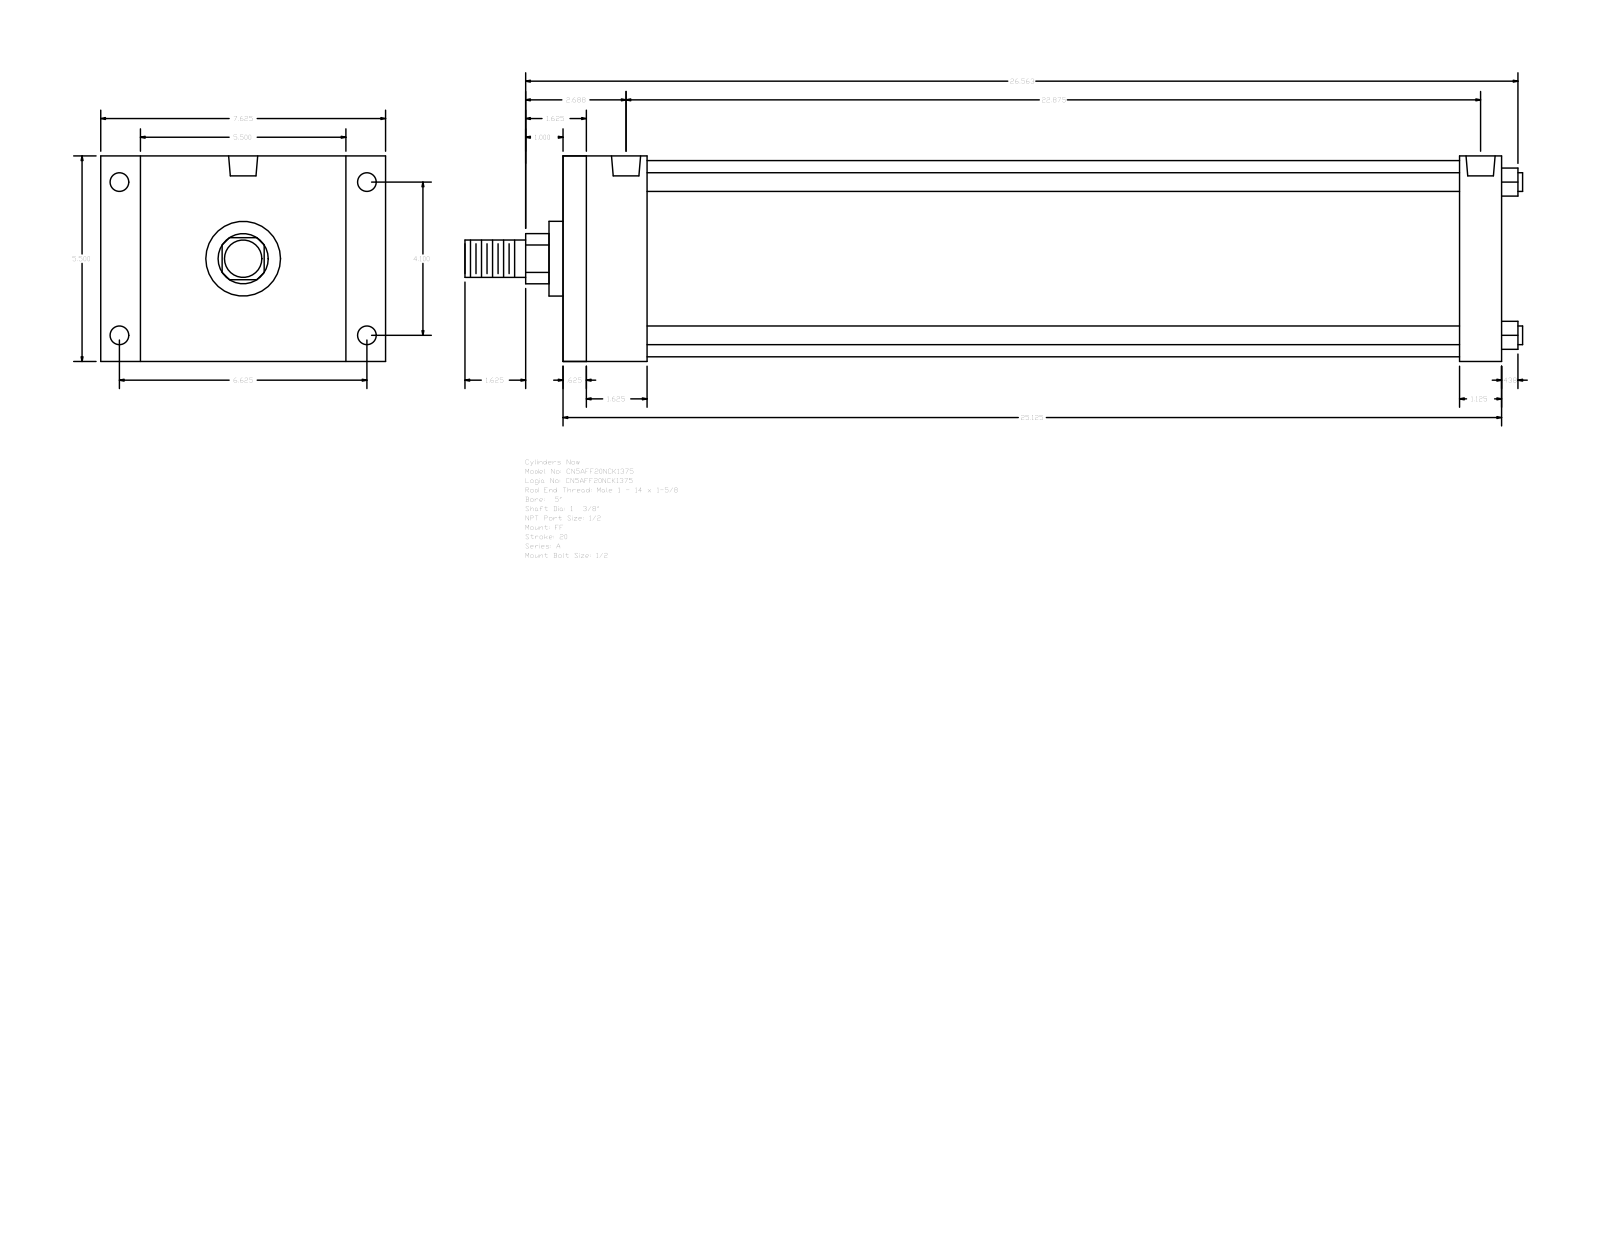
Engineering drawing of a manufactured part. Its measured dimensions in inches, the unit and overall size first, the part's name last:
Units: inches
Overall size (bounding box): 28.313 × 7.625 × 5.5
Round holes (diameter × count): ⌀0.344 ×4, ⌀0.5 ×4, ⌀0.778 ×2
Round bosses / shafts (diameter × count): ⌀0.5 ×4, ⌀5.25 ×1, ⌀2 ×1, ⌀1.375 ×1, ⌀1 ×1
Partial cylindrical surfaces — rounded edges, fillets, slot ends (radius × count): R0.672 ×1
Main face-to-face distances: 5.5, 25.125, 0.625, 24.5, 2.25, 1.125, 24, 23.375, 1.625, 21.75
Hole centre spacings: 0.094, 4.1, 6.625, 7.791, 22.687, 22.781, 22.875
Bodies: 0 solids, 92 faces (64 planar, 28 cylindrical, 0 other)
Part name (STEP PRODUCT): A_FF__0500_1.375
STEP written by: GSSL Pune (CONFIG_CONTROL_DESIGN)
